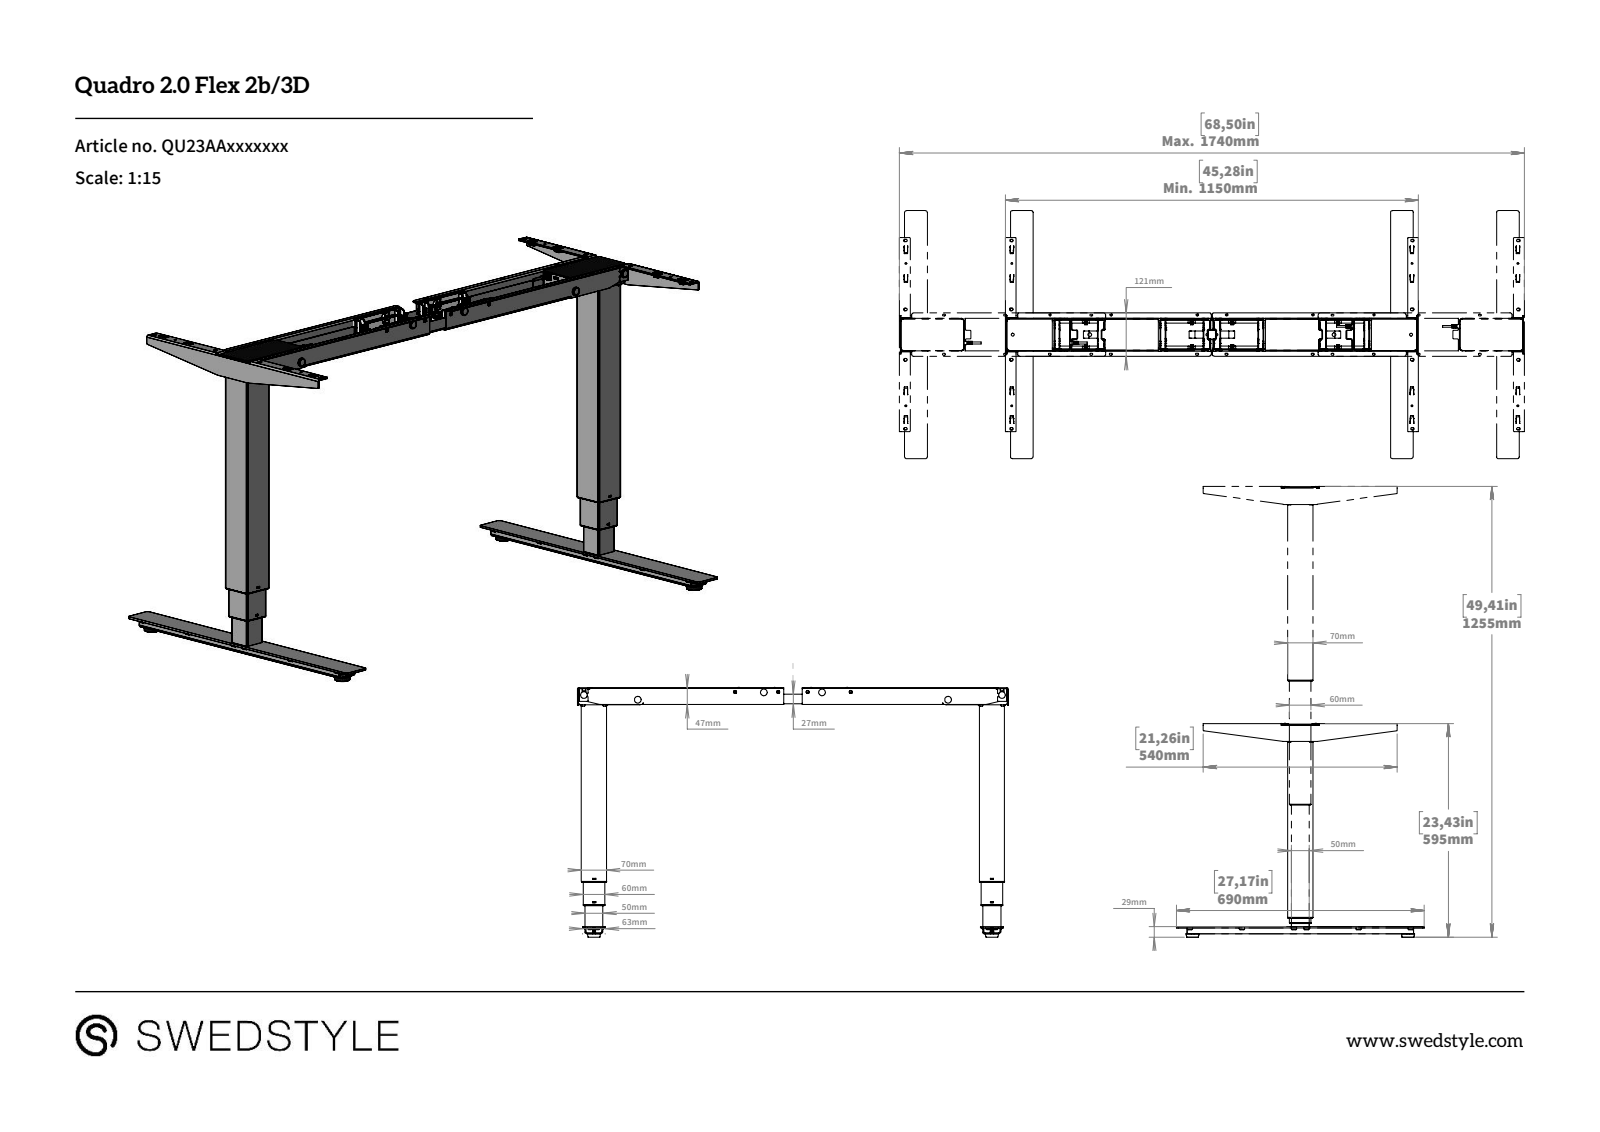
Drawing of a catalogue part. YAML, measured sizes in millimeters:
part_name: "QU23AAxxxxxxx_Fl115"
step_written_by: "SolidWorks 2015 (CONFIG_CONTROL_DESIGN)"
units: millimeters
bodies: {solids: 0, faces: 1580, planar: 754, cylindrical: 614, other: 212}
overall_size: [1200, 694.7, 690]
round_holes:
  - {diameter: 8, count: 8}
  - {diameter: 16, count: 8}
  - {diameter: 5, count: 4}
  - {diameter: 14, count: 4}
  - {diameter: 6, count: 2}
  - {diameter: 7, count: 2}
  - {diameter: 10, count: 2}
round_bosses_or_shafts:
  - {diameter: 8.5, count: 2}
  - {diameter: 5.5, count: 2}
partial_cylinders:
  - {radius: 0.5, count: 94}
  - {radius: 2.5, count: 74}
  - {radius: 1, count: 38}
  - {radius: 2, count: 36}
  - {radius: 2.75, count: 24}
  - {radius: 4, count: 20}
  - {radius: 3, count: 18}
  - {radius: 3.5, count: 16}
face_to_face_distances: [2, 4, 70, 622.1, 2.5, 0.5, 10, 1108, 90.5, 8]
hole_center_spacings: [203.3, 237.26, 1108, 22, 34, 35.61, 40.5, 181.8]
